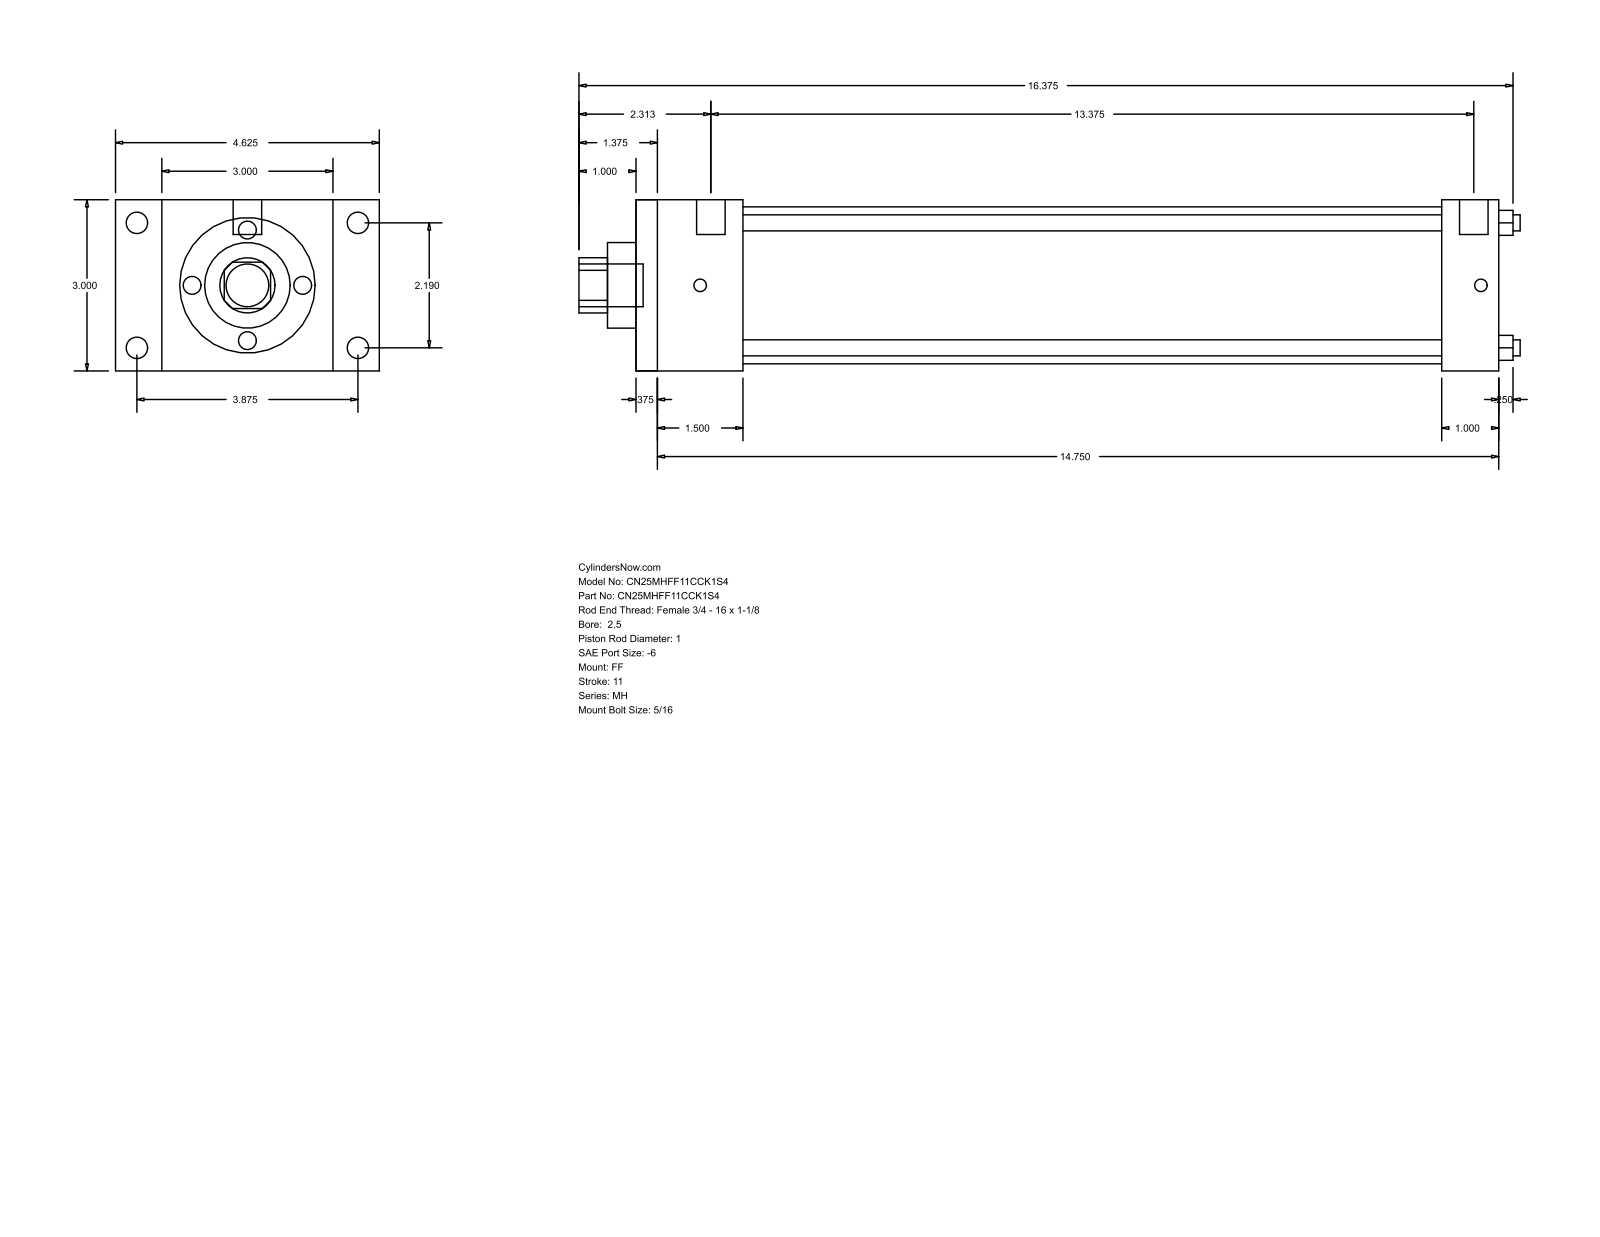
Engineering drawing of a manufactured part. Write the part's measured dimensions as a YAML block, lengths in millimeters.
part_name: "MH_FF__0250_1"
step_written_by: "GSSL Pune (CONFIG_CONTROL_DESIGN)"
units: millimeters
bodies: {solids: 0, faces: 92, planar: 64, cylindrical: 28, other: 0}
overall_size: [419.1, 117.47, 76.2]
round_holes:
  - {diameter: 7.14, count: 4}
  - {diameter: 25.4, count: 1}
  - {diameter: 38.1, count: 1}
  - {diameter: 69.85, count: 1}
round_bosses_or_shafts:
  - {diameter: 9.53, count: 4}
  - {diameter: 5.56, count: 4}
  - {diameter: 12.7, count: 2}
  - {diameter: 19.05, count: 1}
partial_cylinders:
  - {radius: 12.29, count: 1}
face_to_face_distances: [76.2, 384.17, 374.65, 9.52, 25.39, 47.63, 358.78, 38.11, 349.26, 311.15]
hole_center_spacings: [39.33, 55.62, 78.66]
